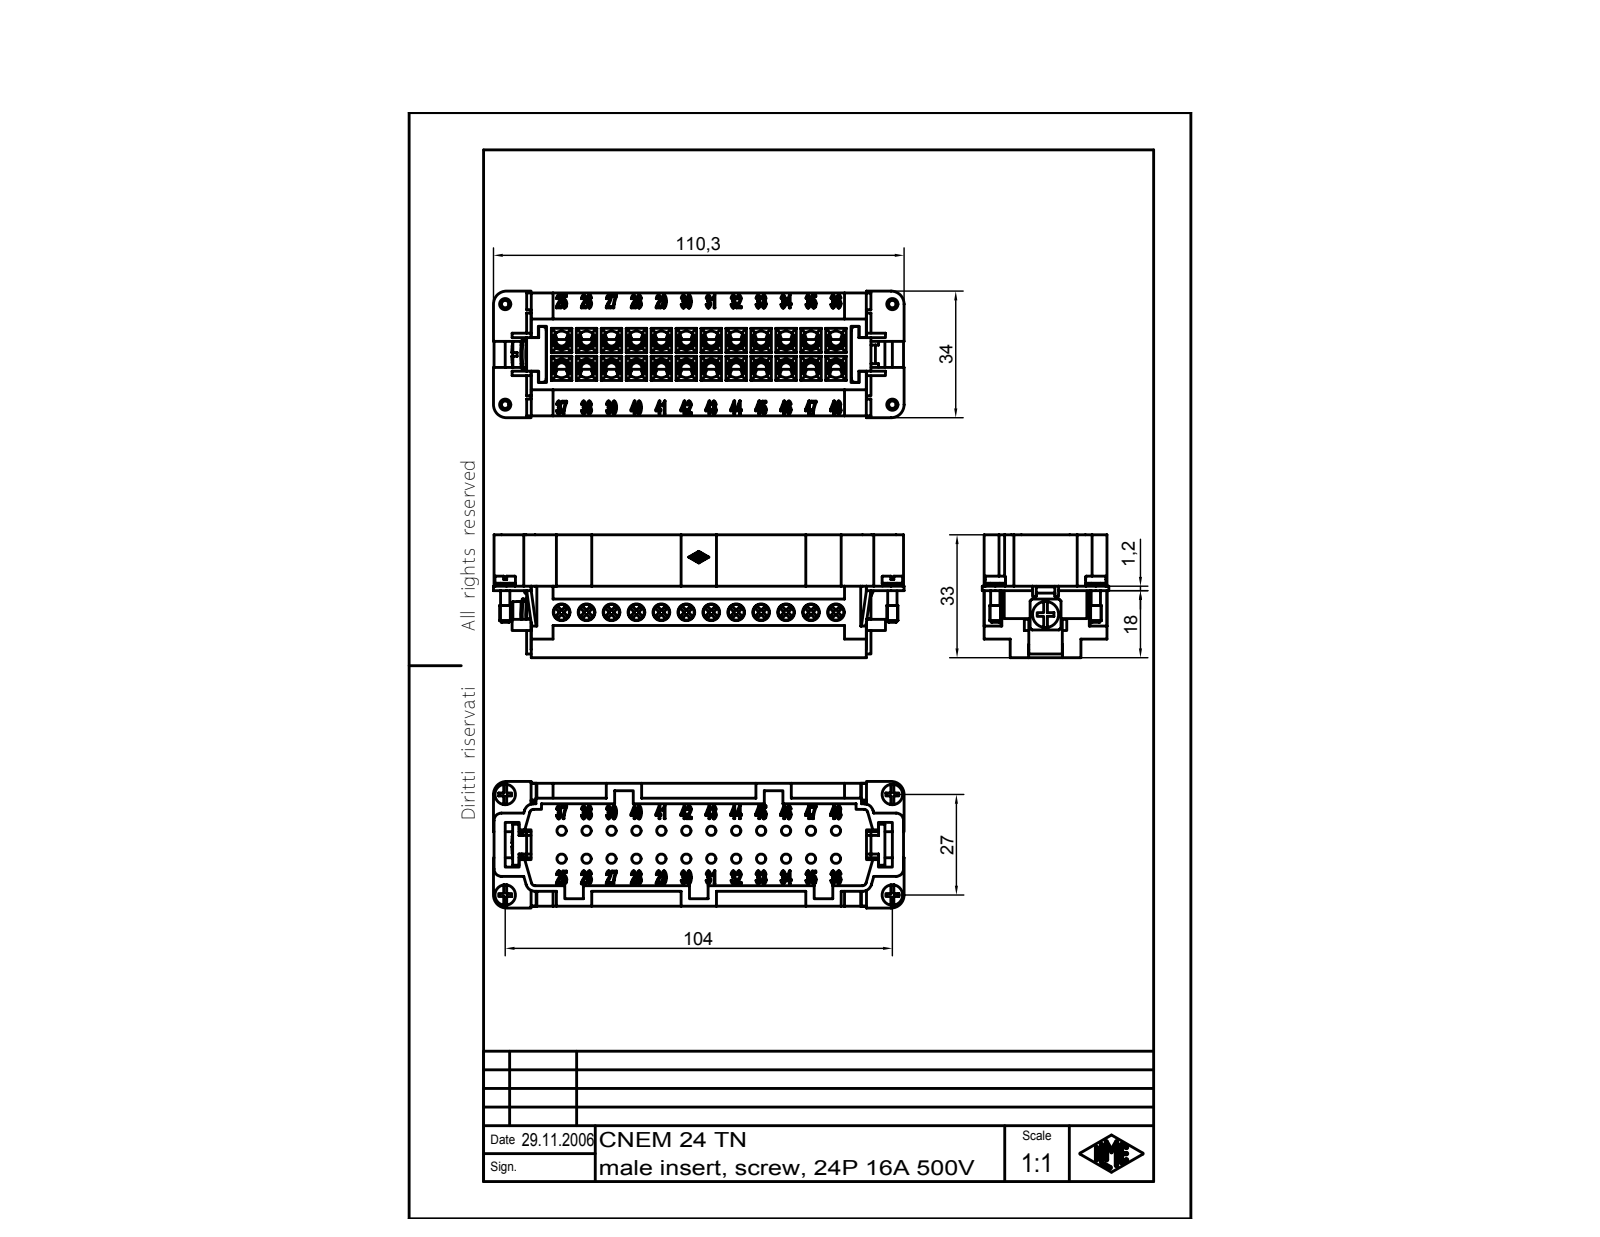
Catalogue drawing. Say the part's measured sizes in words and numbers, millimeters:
The part is named "CNEM 24 TN". Its 3-D file was written by "Autodesk Inventor 7 (AUTOMOTIVE_DESIGN)". It is 1 solid with 3017 faces: 1329 planar, 222 cylindrical and 1466 other. Overall it measures 110.3 by 34 by 33 millimeters. Its volume is 48 904 cubic millimeters and its surface area 38 565 square millimeters. Round holes: 12 of diameter 3, 12 of diameter 4.5, 12 of diameter 5, 2 of diameter 2.55, 1 of diameter 3.24. Round bosses or shafts: 14 of diameter 2.5, 12 of diameter 4.2, 2 of diameter 5.5, 2 of diameter 5.3, 2 of diameter 3, 1 of diameter 7. Partial cylindrical surfaces (rounded edges, fillets, slot ends): 14 of radius 0.1, 12 of radius 2.1, 6 of radius 1, 6 of radius 2, 4 of radius 2.5, 2 of radius 3.5, 1 of radius 5.5. The main face-to-face distances are 1.5, 22, 3, 20.5, 4, 7, 5.5, 23.5, 29, 26. The hole center spacings are 6.7, 13.4, 20.1, 26.8, 33.5, 40.2, 46.9, 53.6.
